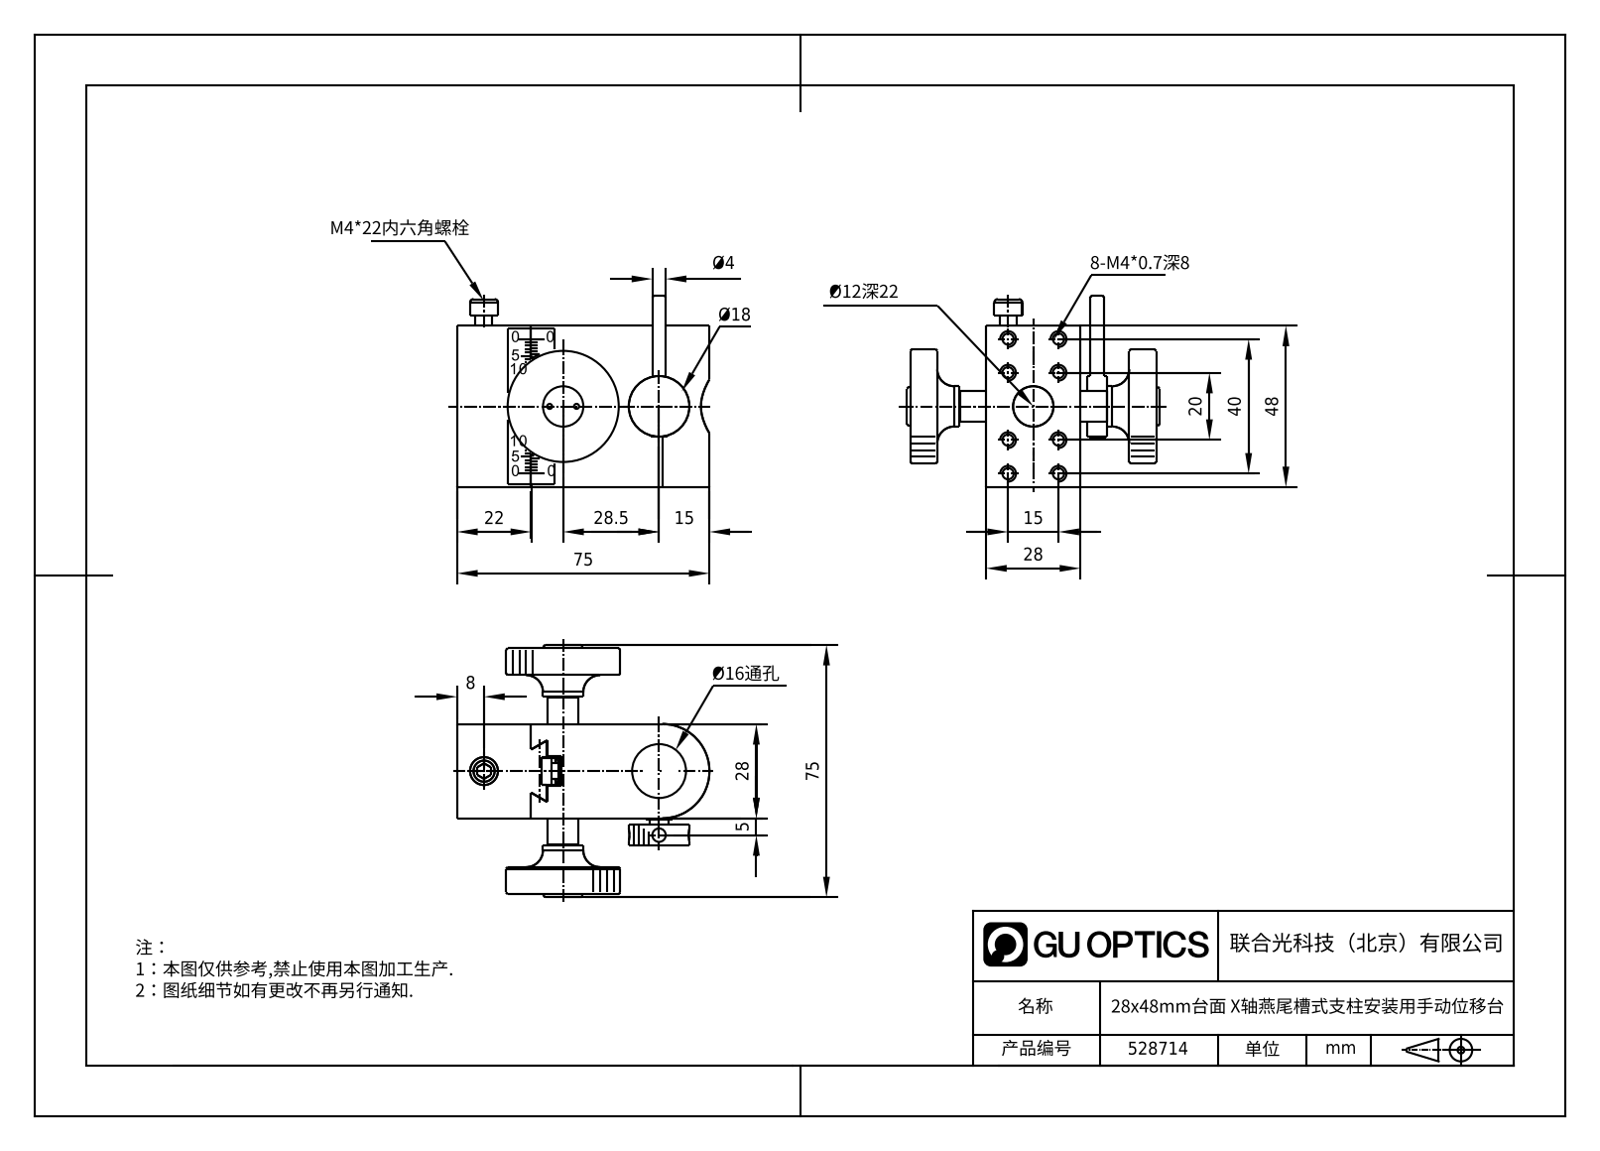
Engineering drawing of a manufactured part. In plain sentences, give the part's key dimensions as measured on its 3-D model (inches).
The part is named "528714". Its 3-D file was written by "SolidWorks 2020 (CONFIG_CONTROL_DESIGN)". It is 2 solids with 163 faces: 72 planar, 48 cylindrical and 43 other. Overall it measures 2.953 by 2.941 by 2.224 inches. Its volume is 5.938 cubic inches and its surface area 47.94 square inches. Round holes: 9 of diameter 0.128, 5 of diameter 0.079, 3 of diameter 0.079, 2 of diameter 0.098, 2 of diameter 0.63, 1 of diameter 0.268, 1 of diameter 0.276, 1 of diameter 0.335, 1 of diameter 0.472. Round bosses or shafts: 2 of diameter 0.157, 1 of diameter 1.339, 1 of diameter 0.709, 1 of diameter 0.472, 1 of diameter 0.457, 1 of diameter 0.37, 1 of diameter 0.346, 1 of diameter 0.335. Partial cylindrical surfaces (rounded edges, fillets, slot ends): 1 of radius 0.551. The main face-to-face distances are 1.102, 1.988, 1.89, 0.886, 0.866, 0.315, 0.571, 2.559, 1.673, 2.874. The hole center spacings are 0.301, 0.394, 0.492, 0.541, 0.591, 0.71, 0.841, 1.181.
